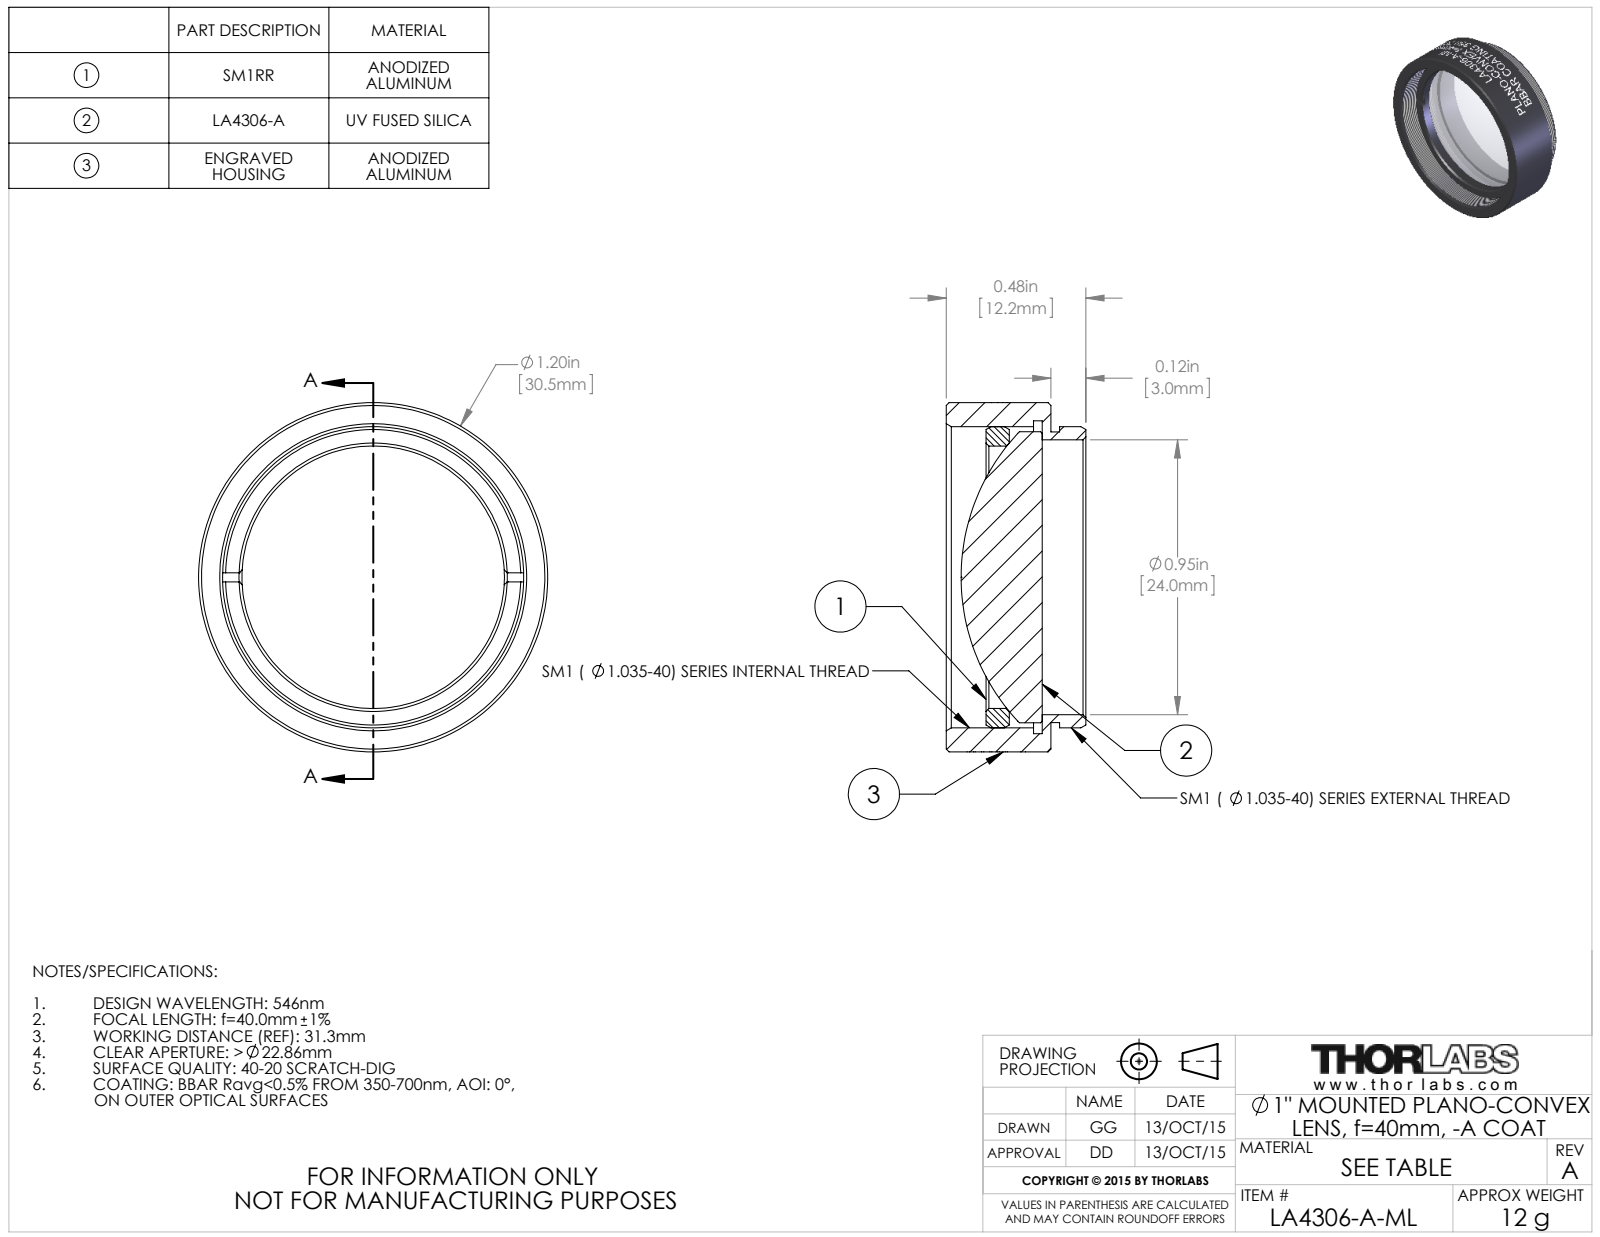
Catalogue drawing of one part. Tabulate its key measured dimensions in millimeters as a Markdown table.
| quantity | value |
| --- | --- |
| part name | TTN039228-E0W |
| STEP written by | SolidWorks 2014 (CONFIG_CONTROL_DESIGN) |
| units | millimeters |
| bodies | 3 solids, 161 faces (20 planar, 113 cylindrical, 28 other) |
| overall size | 30.48 × 30.48 × 12.19 |
| volume | 4 592 mm³ |
| surface area | 4 523 mm² |
| round holes (diameter × count) | 22.91 × 1, 24 × 1, 27.3 × 1 |
| round bosses / shafts (diameter × count) | 30.48 × 1, 26.29 × 1, 25.4 × 1, 25.37 × 1 |
| main face-to-face distances | 0.76, 9.15, 8.39, 3.64, 2.88, 5.51, 5.67, 4.91, 2.03, 3.48 |
